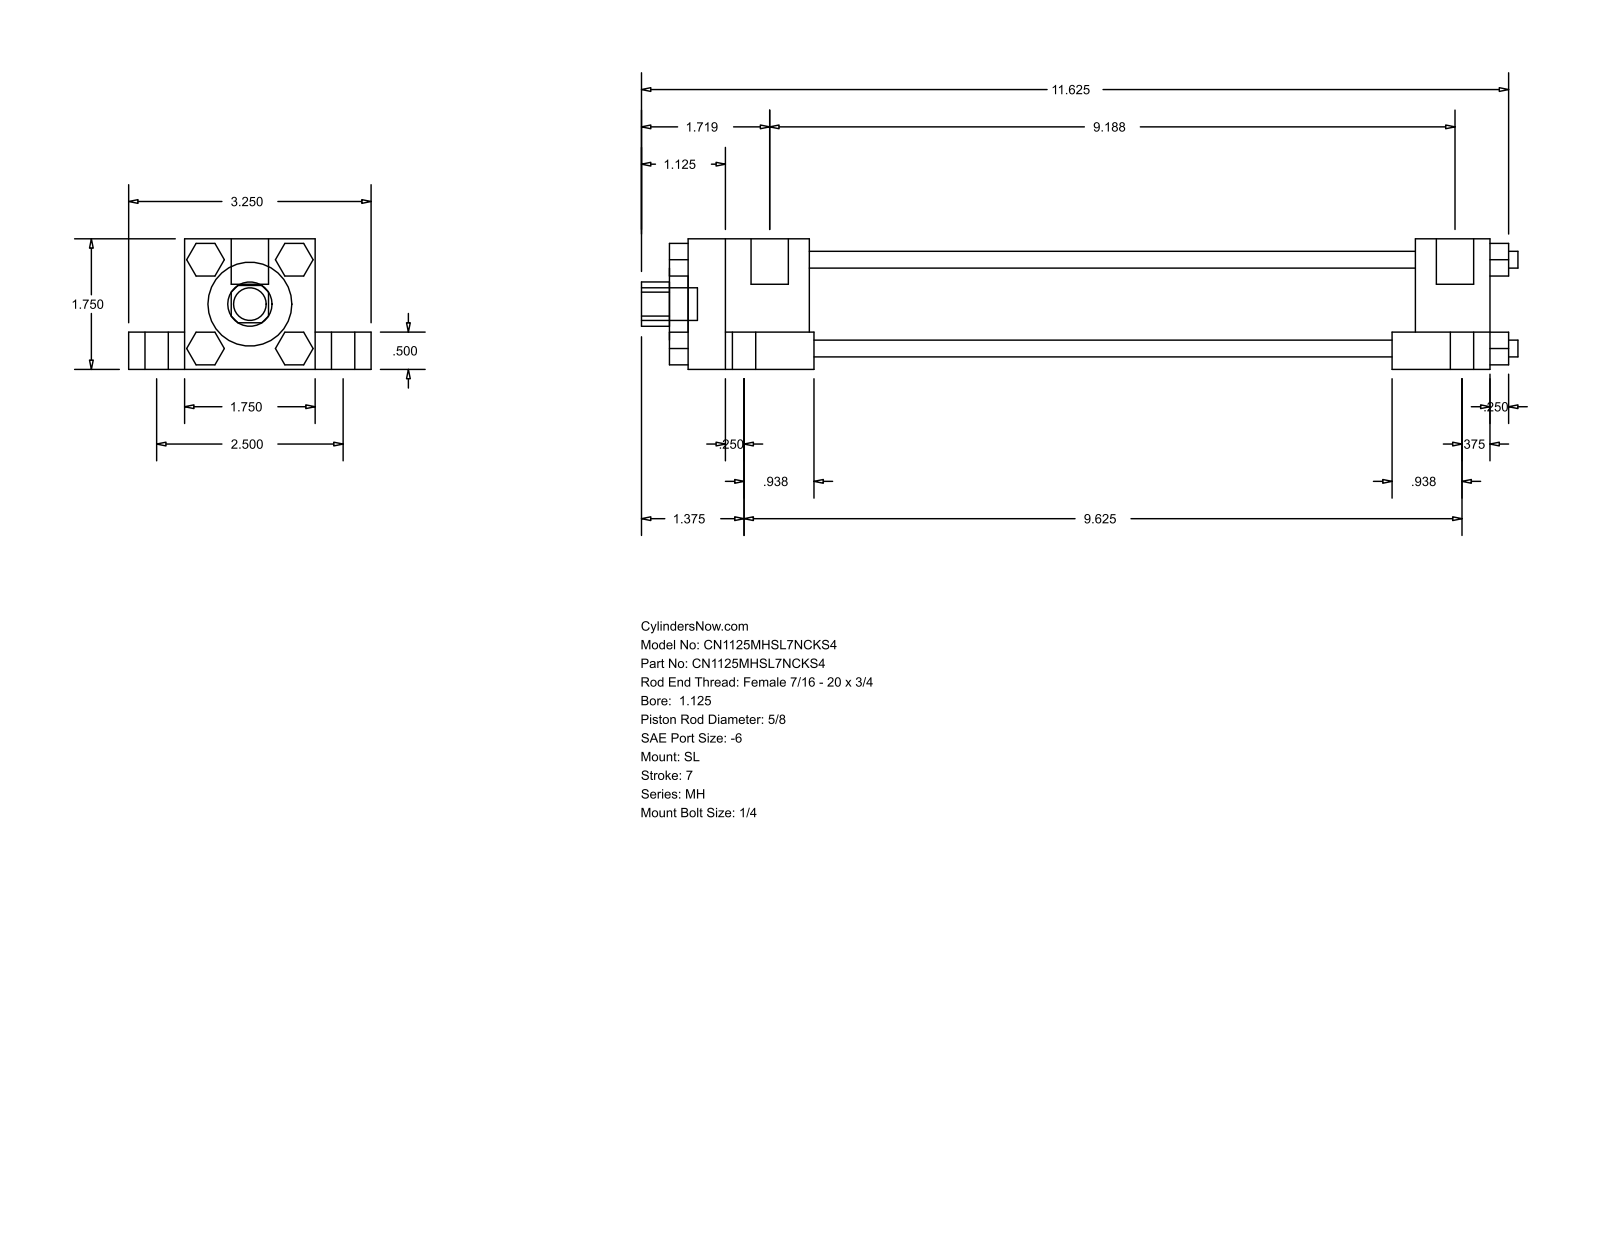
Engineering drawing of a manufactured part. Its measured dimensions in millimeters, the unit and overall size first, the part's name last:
Units: millimetres
Overall size (bounding box): 298.45 × 82.55 × 44.45
Round holes (diameter × count): ⌀15.88 ×1, ⌀28.57 ×1, ⌀34.92 ×1
Round bosses / shafts (diameter × count): ⌀14.29 ×4, ⌀7.94 ×4, ⌀5.71 ×4, ⌀5.56 ×4, ⌀12.7 ×2, ⌀11.11 ×1
Partial cylindrical surfaces — rounded edges, fillets, slot ends (radius × count): R7.54 ×1
Main face-to-face distances: 44.46, 19.04, 12.7, 31.76, 63.5, 11.11, 33.34, 227.02, 206.37, 231.78
Bodies: 0 solids, 150 faces (114 planar, 36 cylindrical, 0 other)
Part name (STEP PRODUCT): MH_SL__0112_0.625
STEP written by: GSSL Pune (CONFIG_CONTROL_DESIGN)
